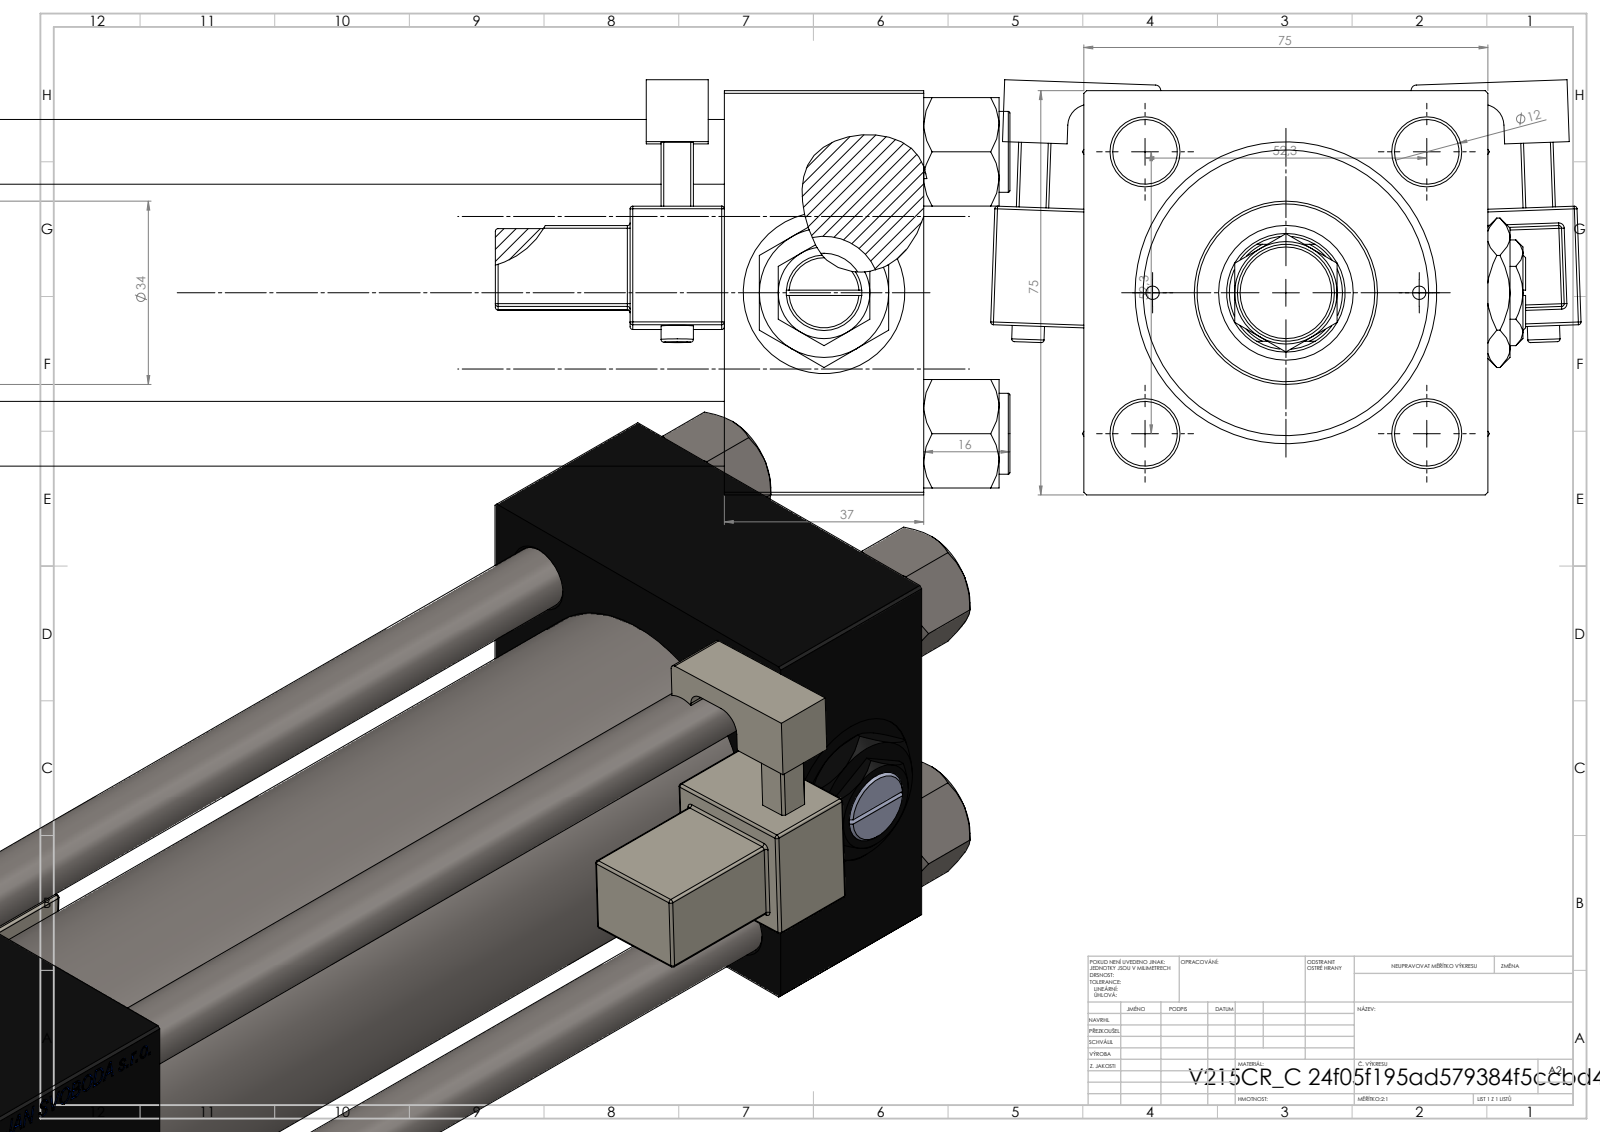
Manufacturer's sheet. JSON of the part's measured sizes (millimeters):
{"part_name": "V215CR_C_TYCINKA; V215CR_MSU; Zatka_pro_OIL_PORT; NUT_M5_C (+4 more)", "step_written_by": "SolidWorks 2019 (CONFIG_CONTROL_DESIGN)", "units": "millimeters", "bodies": {"solids": 16, "faces": 1461, "planar": 649, "cylindrical": 166, "other": 646}, "overall_size": [333, 109.57, 77.03], "volume_mm3": 840867, "surface_area_mm2": 224864, "round_holes": [[12, 4], [2.5, 2], [7, 2], [20.96, 2], [30, 2], [10.5, 1], [22, 1], [25, 1], [41, 1], [50, 1], [53, 1]], "round_bosses_or_shafts": [[15, 4], [6, 2], [56, 1], [34, 1], [18, 1], [11, 1]], "partial_cylinders_radius": [[0.5, 48], [1, 2], [2.5, 2], [4, 2], [10.5, 1]], "face_to_face_distances": [75, 37, 259, 222, 200, 163, 59, 230.3, 193.3, 30.3], "hole_center_spacings": [26.19, 36.98, 52.3, 57.22, 24.75, 73.96, 49.5, 198.5]}
